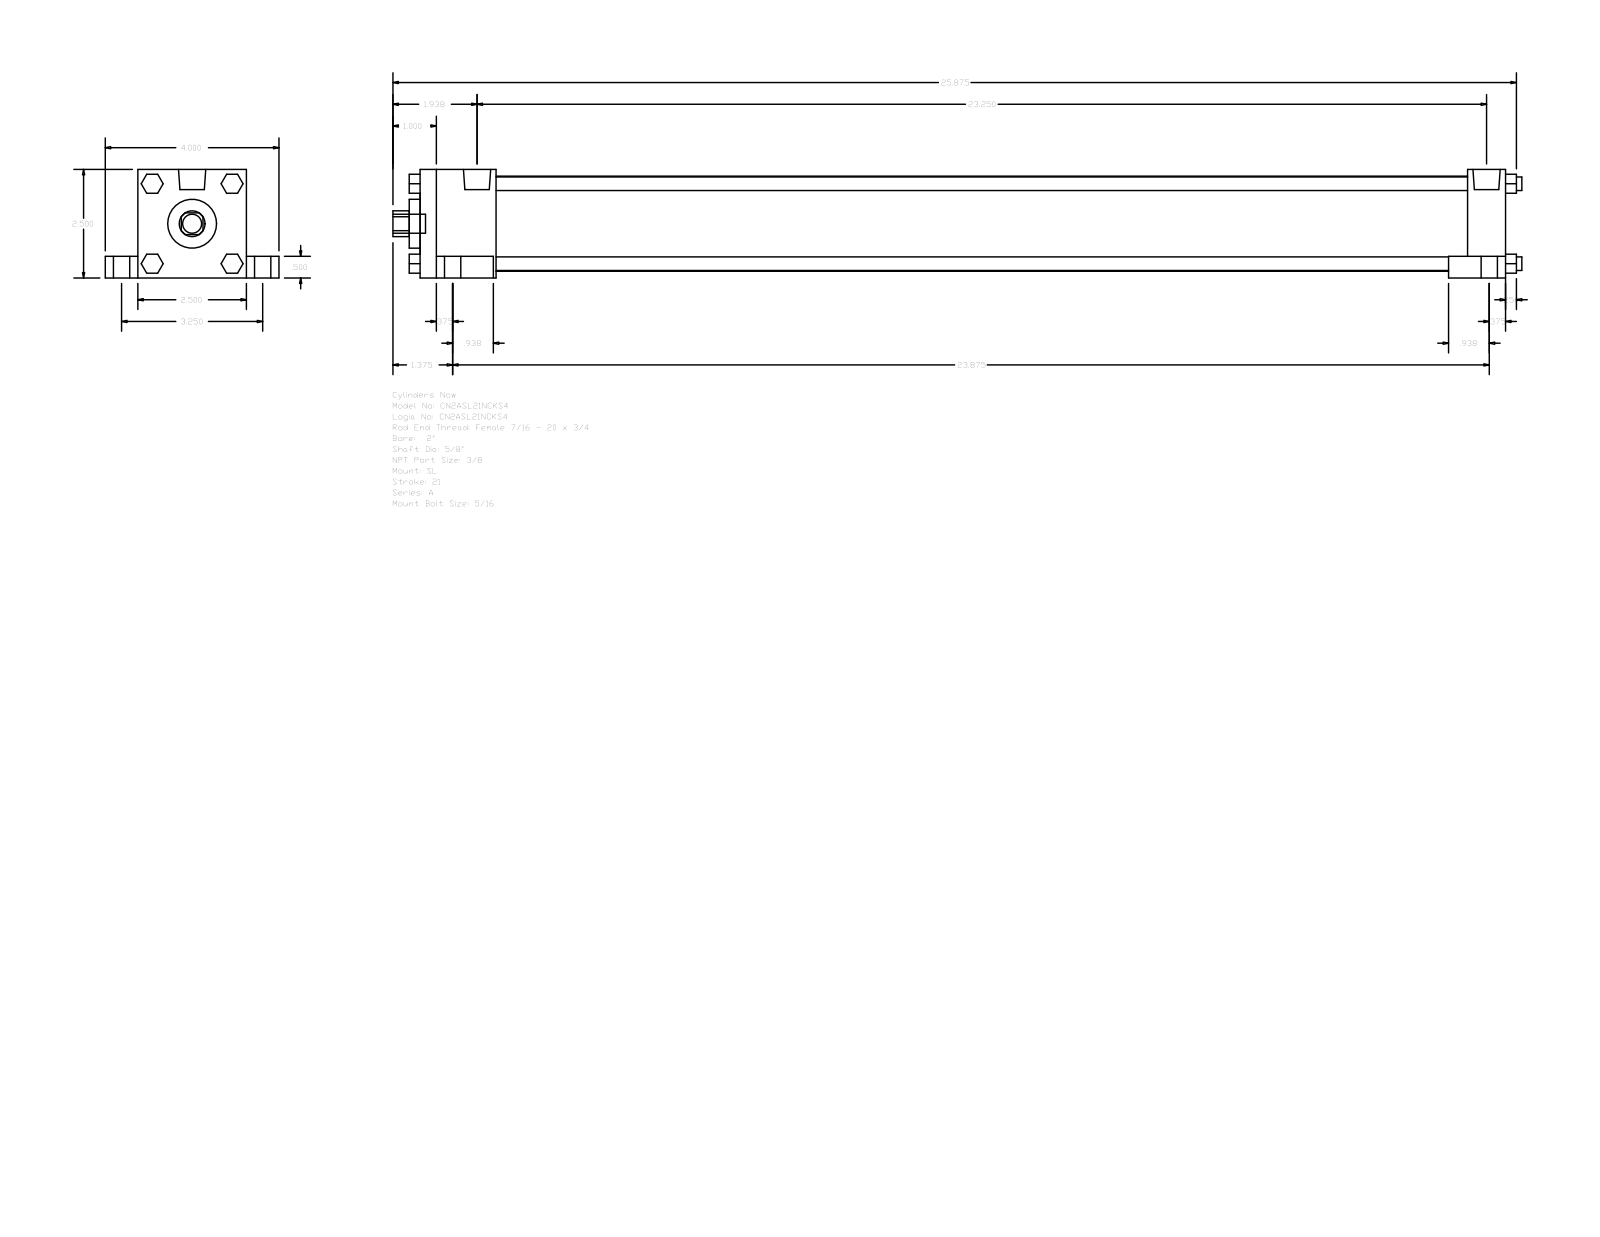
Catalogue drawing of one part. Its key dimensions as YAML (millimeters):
part_name: "A_SL__0200_0.625"
step_written_by: "GSSL Pune (CONFIG_CONTROL_DESIGN)"
units: millimeters
bodies: {solids: 0, faces: 148, planar: 112, cylindrical: 36, other: 0}
overall_size: [660.4, 101.6, 63.5]
round_holes:
  - {diameter: 15.88, count: 1}
  - {diameter: 28.57, count: 1}
  - {diameter: 55.63, count: 1}
round_bosses_or_shafts:
  - {diameter: 15.88, count: 4}
  - {diameter: 9.53, count: 4}
  - {diameter: 7.94, count: 4}
  - {diameter: 5.56, count: 4}
  - {diameter: 15.93, count: 2}
  - {diameter: 11.11, count: 1}
partial_cylinders:
  - {radius: 7.54, count: 1}
face_to_face_distances: [63.5, 635, 50.8, 12.7, 19.05, 82.55, 44.45, 590.55, 612.77, 568.32]
